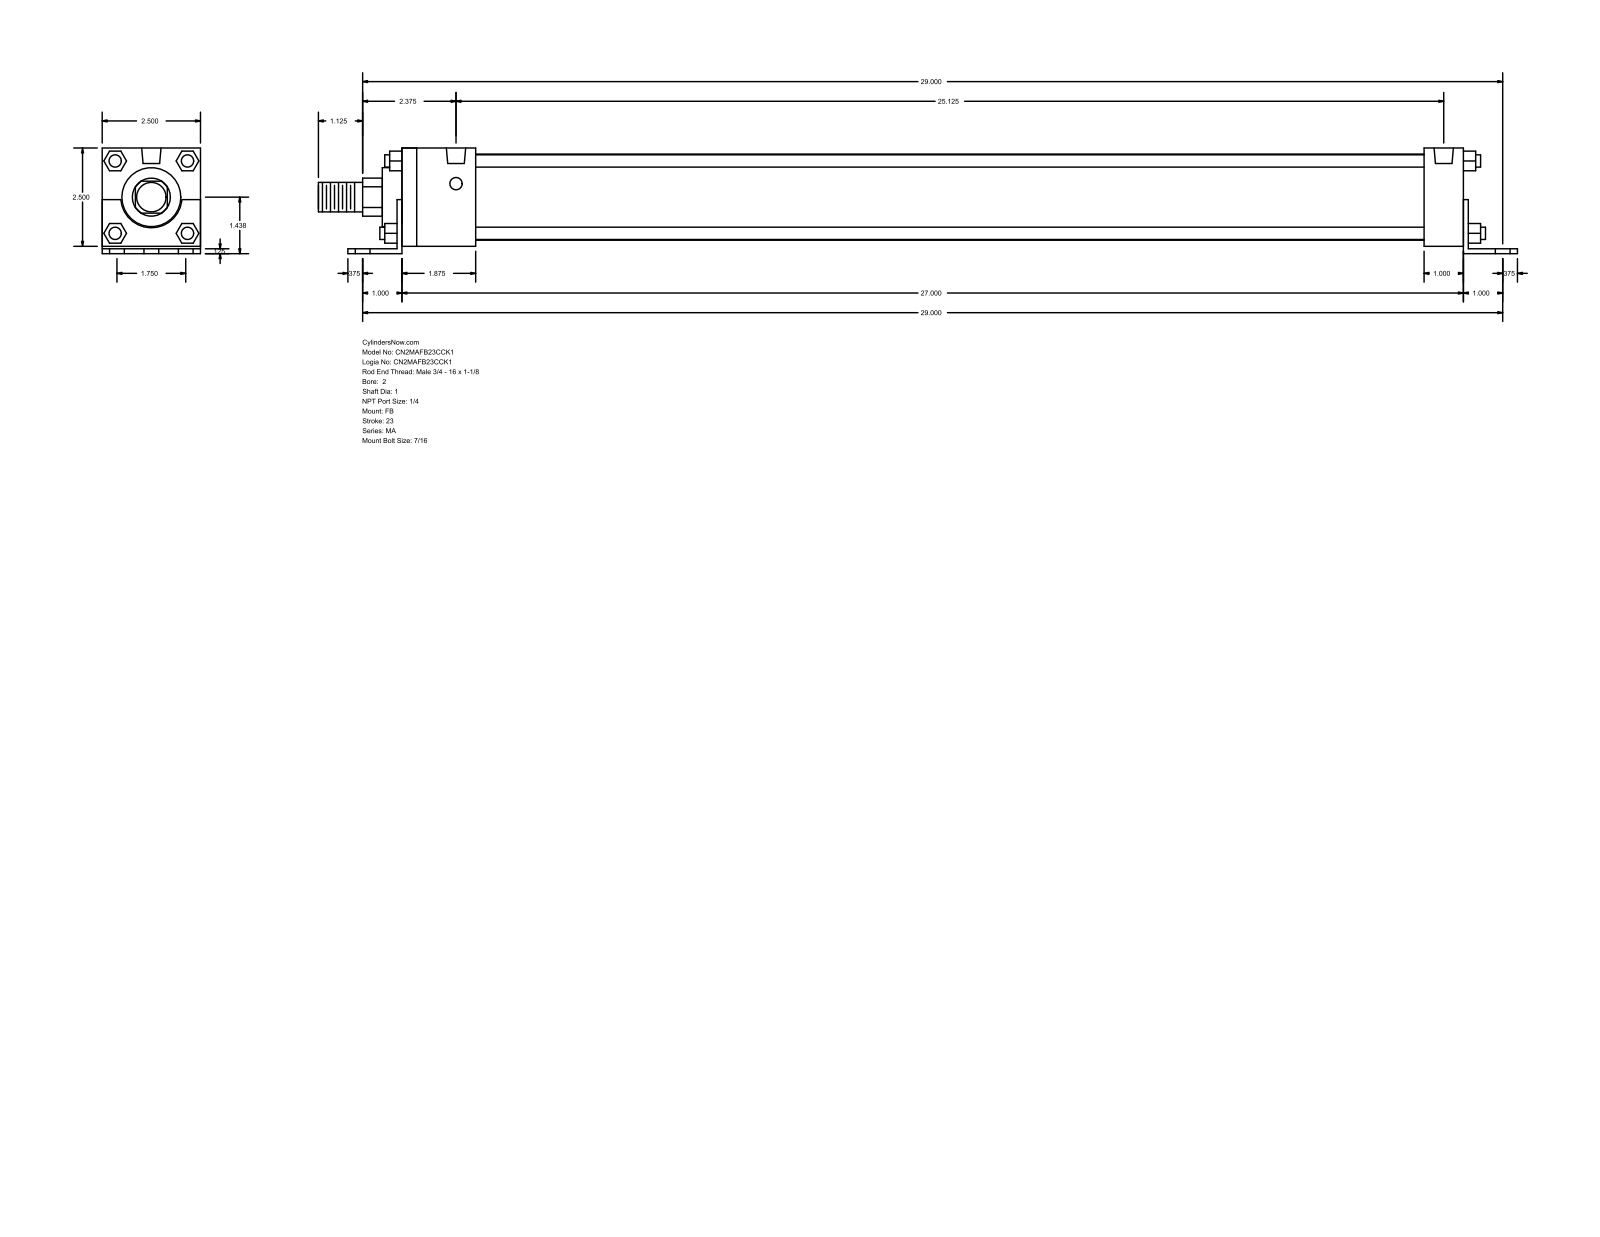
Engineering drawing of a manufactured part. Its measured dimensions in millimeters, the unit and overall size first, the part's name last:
Units: millimetres
Overall size (bounding box): 774.7 × 68.26 × 63.5
Round holes (diameter × count): ⌀11.11 ×6, ⌀7.94 ×4, ⌀12.49 ×2
Round bosses / shafts (diameter × count): ⌀7.94 ×4, ⌀55.63 ×1, ⌀38.1 ×1, ⌀25.4 ×1, ⌀19.05 ×1
Partial cylindrical surfaces — rounded edges, fillets, slot ends (radius × count): R12.29 ×1, R19.81 ×1
Main face-to-face distances: 63.5, 3.17, 4.76, 68.26, 1.59, 65.09, 12.7, 3.18, 685.8, 688.98
Hole centre spacings: 22.23, 736.94, 736.6, 44.11, 44.46, 64.3, 638.17, 676.64
Bodies: 0 solids, 140 faces (105 planar, 35 cylindrical, 0 other)
Part name (STEP PRODUCT): MA_FB__0200_1
STEP written by: GSSL Pune (CONFIG_CONTROL_DESIGN)
